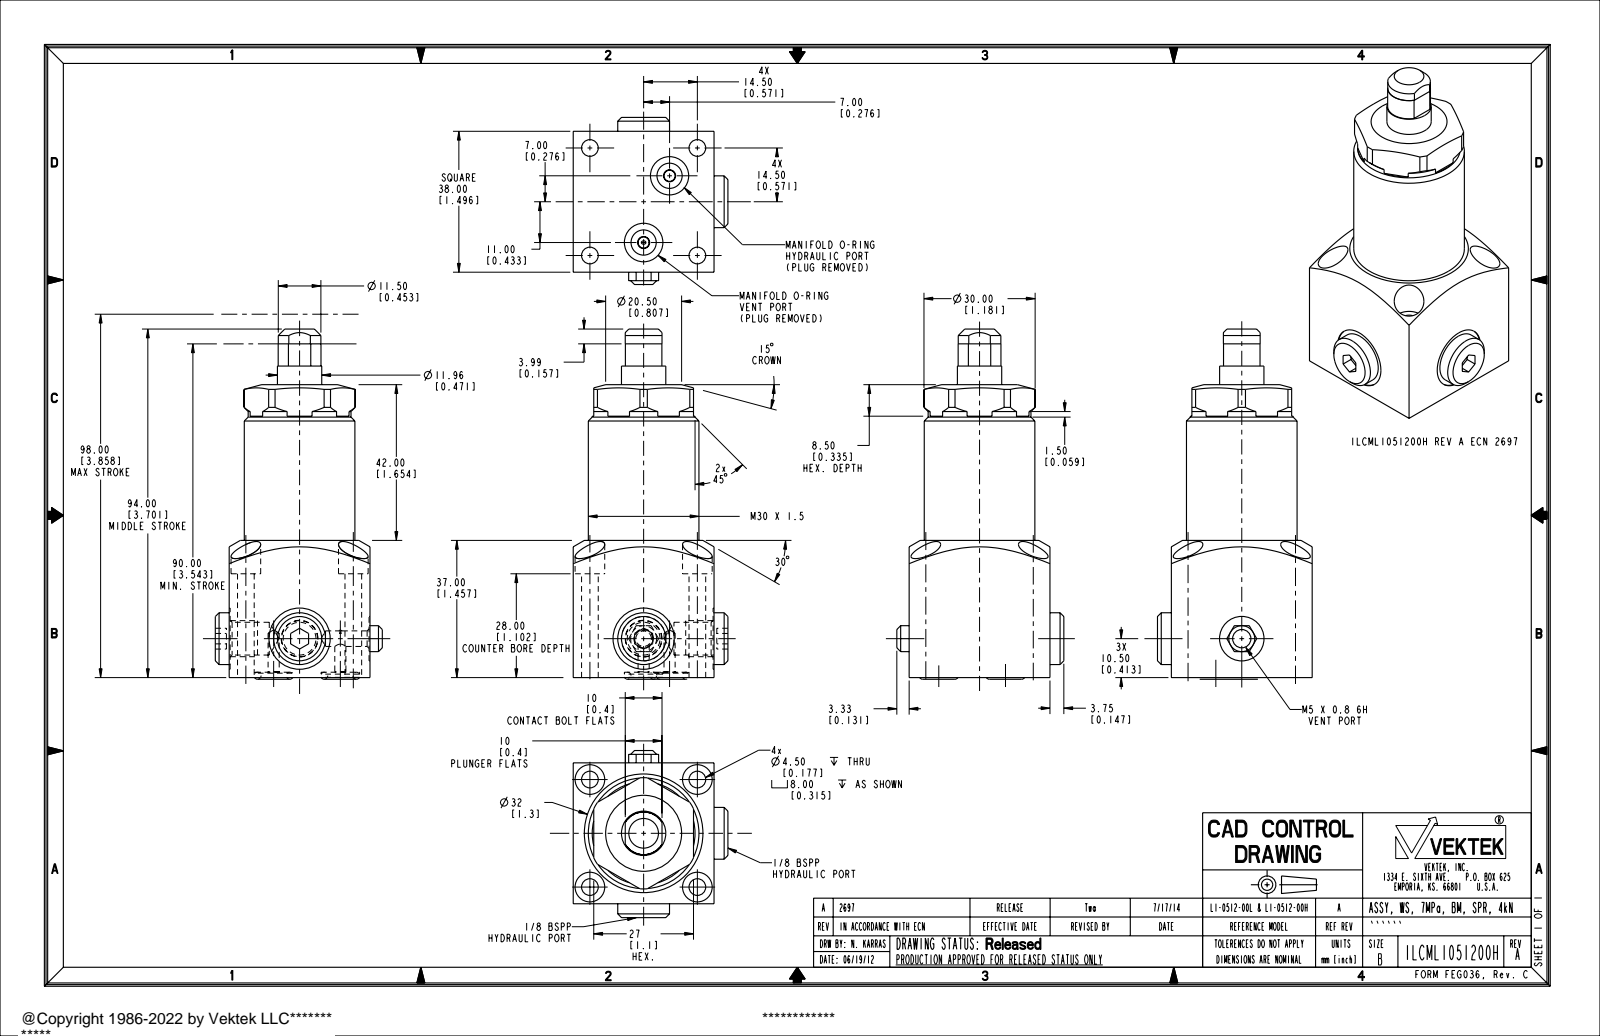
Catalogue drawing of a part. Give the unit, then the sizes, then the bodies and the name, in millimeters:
Units: millimetres
Overall size (bounding box): 94.45 × 45.07 × 41.75
Round holes (diameter × count): ⌀4.5 ×4, ⌀8 ×4, ⌀3 ×2, ⌀8.84 ×2, ⌀16.51 ×2, ⌀4.2 ×1, ⌀10 ×1, ⌀10.39 ×1, ⌀12 ×1
Round bosses / shafts (diameter × count): ⌀13.97 ×2, ⌀9.73 ×2, ⌀29.85 ×1, ⌀27.75 ×1, ⌀11.96 ×1
Partial cylindrical surfaces — rounded edges, fillets, slot ends (radius × count): R5.75 ×1, R5.78 ×1, R15 ×1
Main face-to-face distances: 38, 37.75, 26.92, 79, 41.75, 4, 3.75, 5.54, 32.46, 1.45
Hole centre spacings: 29, 14.92, 22.77, 29.33, 41.01, 10.61, 19.31, 30.41
Volume: 78 330 mm³ · Surface area: 16 980 mm²
Bodies: 1 solid, 182 faces (72 planar, 64 cylindrical, 46 other)
Part name (STEP PRODUCT): ILCML1051200H
STEP written by: PRO/ENGINEER BY PARAMETRIC TECHNOLOGY CORPORATION, 2013320 (AUTOMOTIVE_DESIGN)
